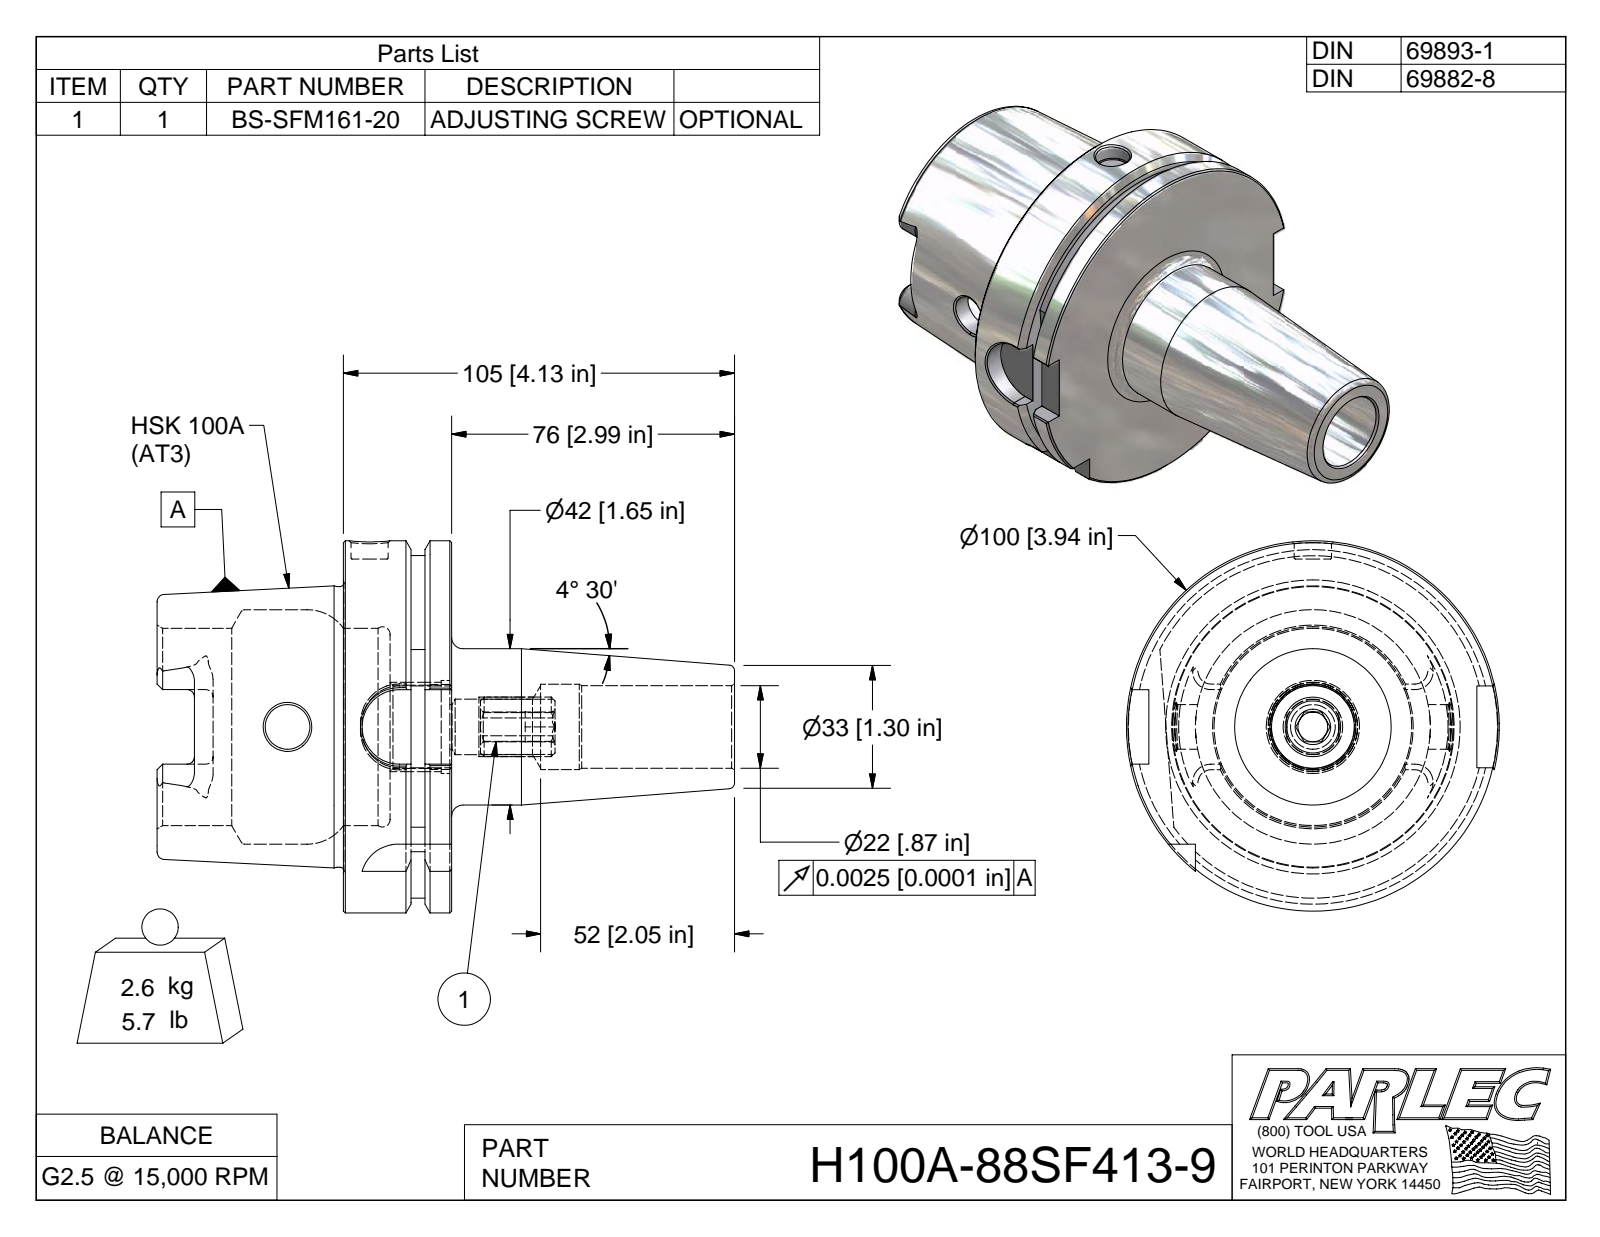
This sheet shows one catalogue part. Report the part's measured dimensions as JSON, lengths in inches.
{"part_name": "H100A-88SF413-9; H100A-88SF413-9-1; BS-SFM161-20", "step_written_by": "Autodesk Inventor 2009 (AUTOMOTIVE_DESIGN)", "units": "inches", "bodies": {"solids": 2, "faces": 149, "planar": 49, "cylindrical": 30, "other": 70}, "overall_size": [6.099, 3.937, 3.937], "volume_in3": 19.61, "surface_area_in2": 100.4, "round_holes": [[0.394, 1], [0.472, 1], [0.874, 1], [0.881, 1], [0.904, 1], [0.985, 1], [2.087, 1], [2.48, 1]], "round_bosses_or_shafts": [[3.937, 1], [2.967, 1], [1.654, 1]], "partial_cylinders_radius": [[0.394, 4], [0.079, 3], [0.192, 2], [0.315, 1], [1.811, 1]], "face_to_face_distances": [1.142, 0.492, 0.65, 1.969, 2.461, 3.11, 2.682, 0.713, 0.221, 0.428]}
